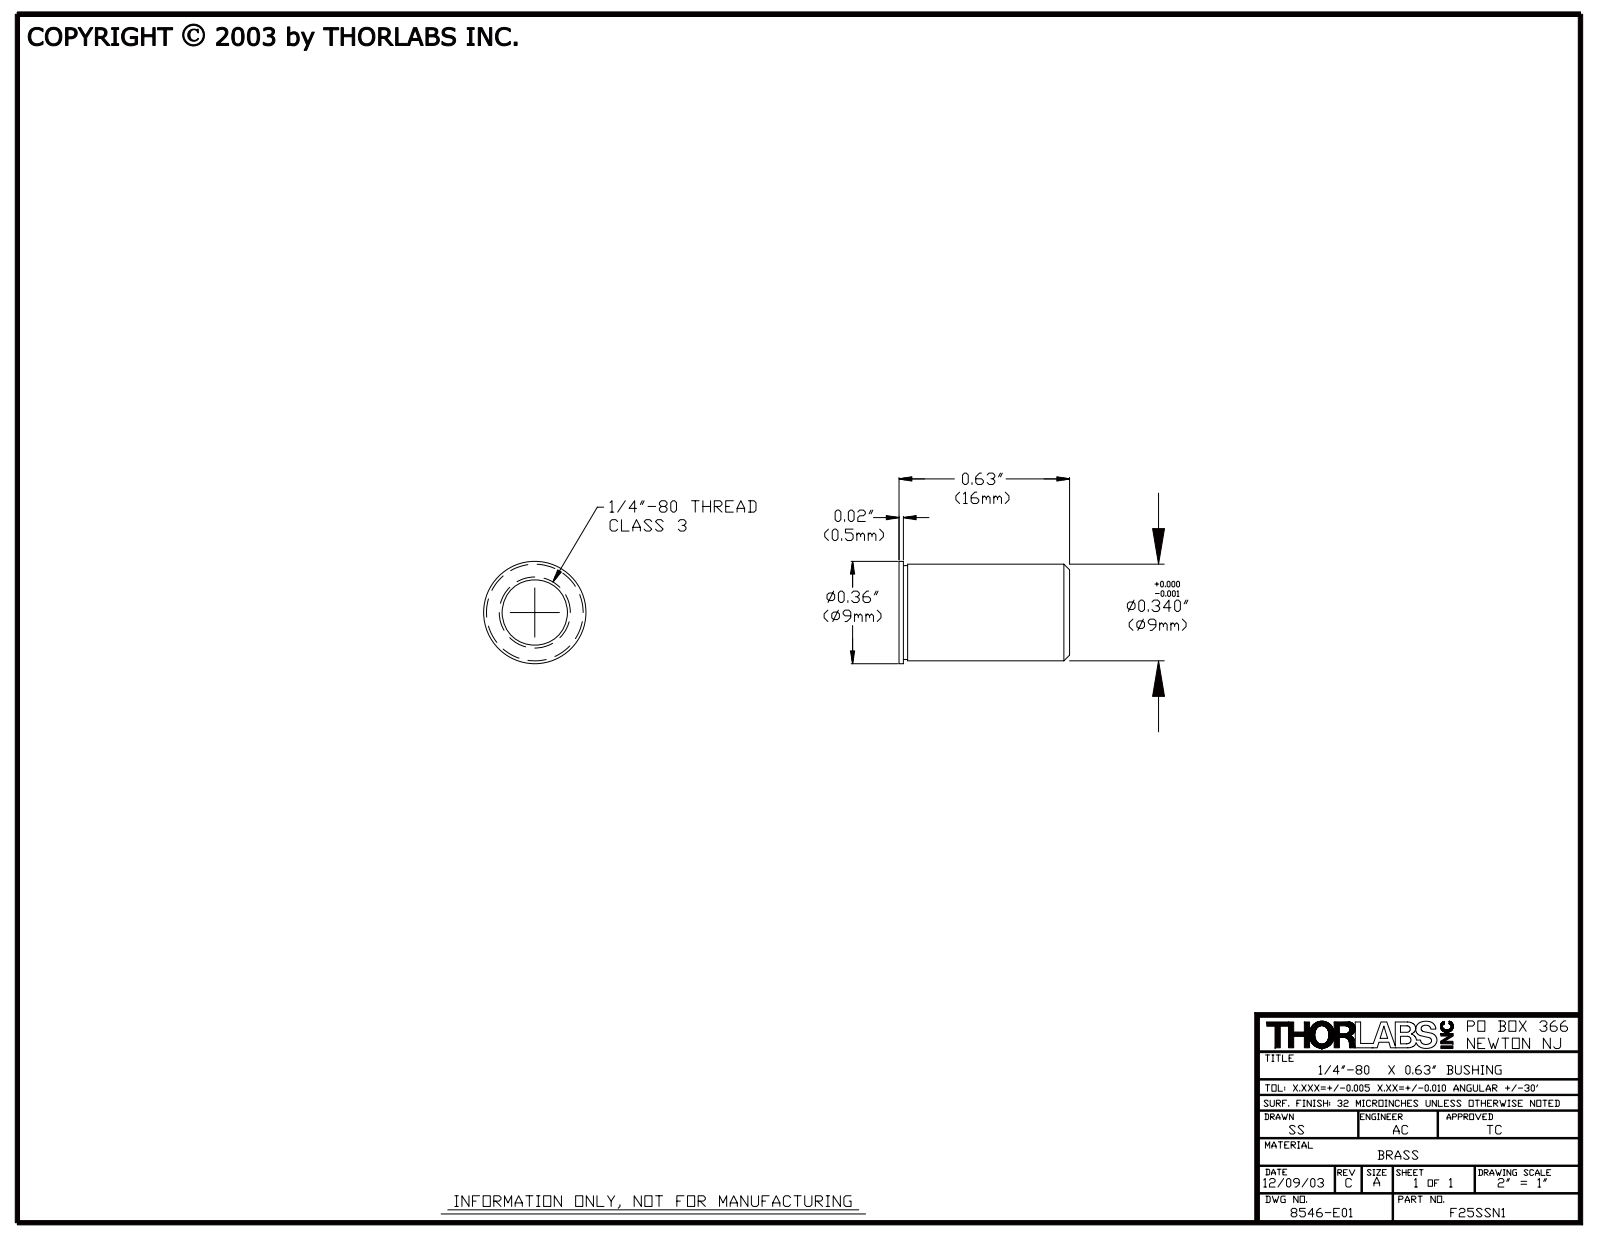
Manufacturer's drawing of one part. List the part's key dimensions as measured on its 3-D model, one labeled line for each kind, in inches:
Part name (STEP PRODUCT): 8546-E0W
STEP written by: SolidWorks 2007 (AUTOMOTIVE_DESIGN)
Units: inches
Bodies: 0 solids, 18 faces (4 planar, 8 cylindrical, 6 other)
Overall size (bounding box): 0.63 × 0.36 × 0.36
Round holes (diameter × count): ⌀0.25 ×1
Round bosses / shafts (diameter × count): ⌀0.36 ×1, ⌀0.34 ×1, ⌀0.32 ×1
Main face-to-face distances: 0.02, 0.63, 0.61, 0.04, 0.02, 0.59
